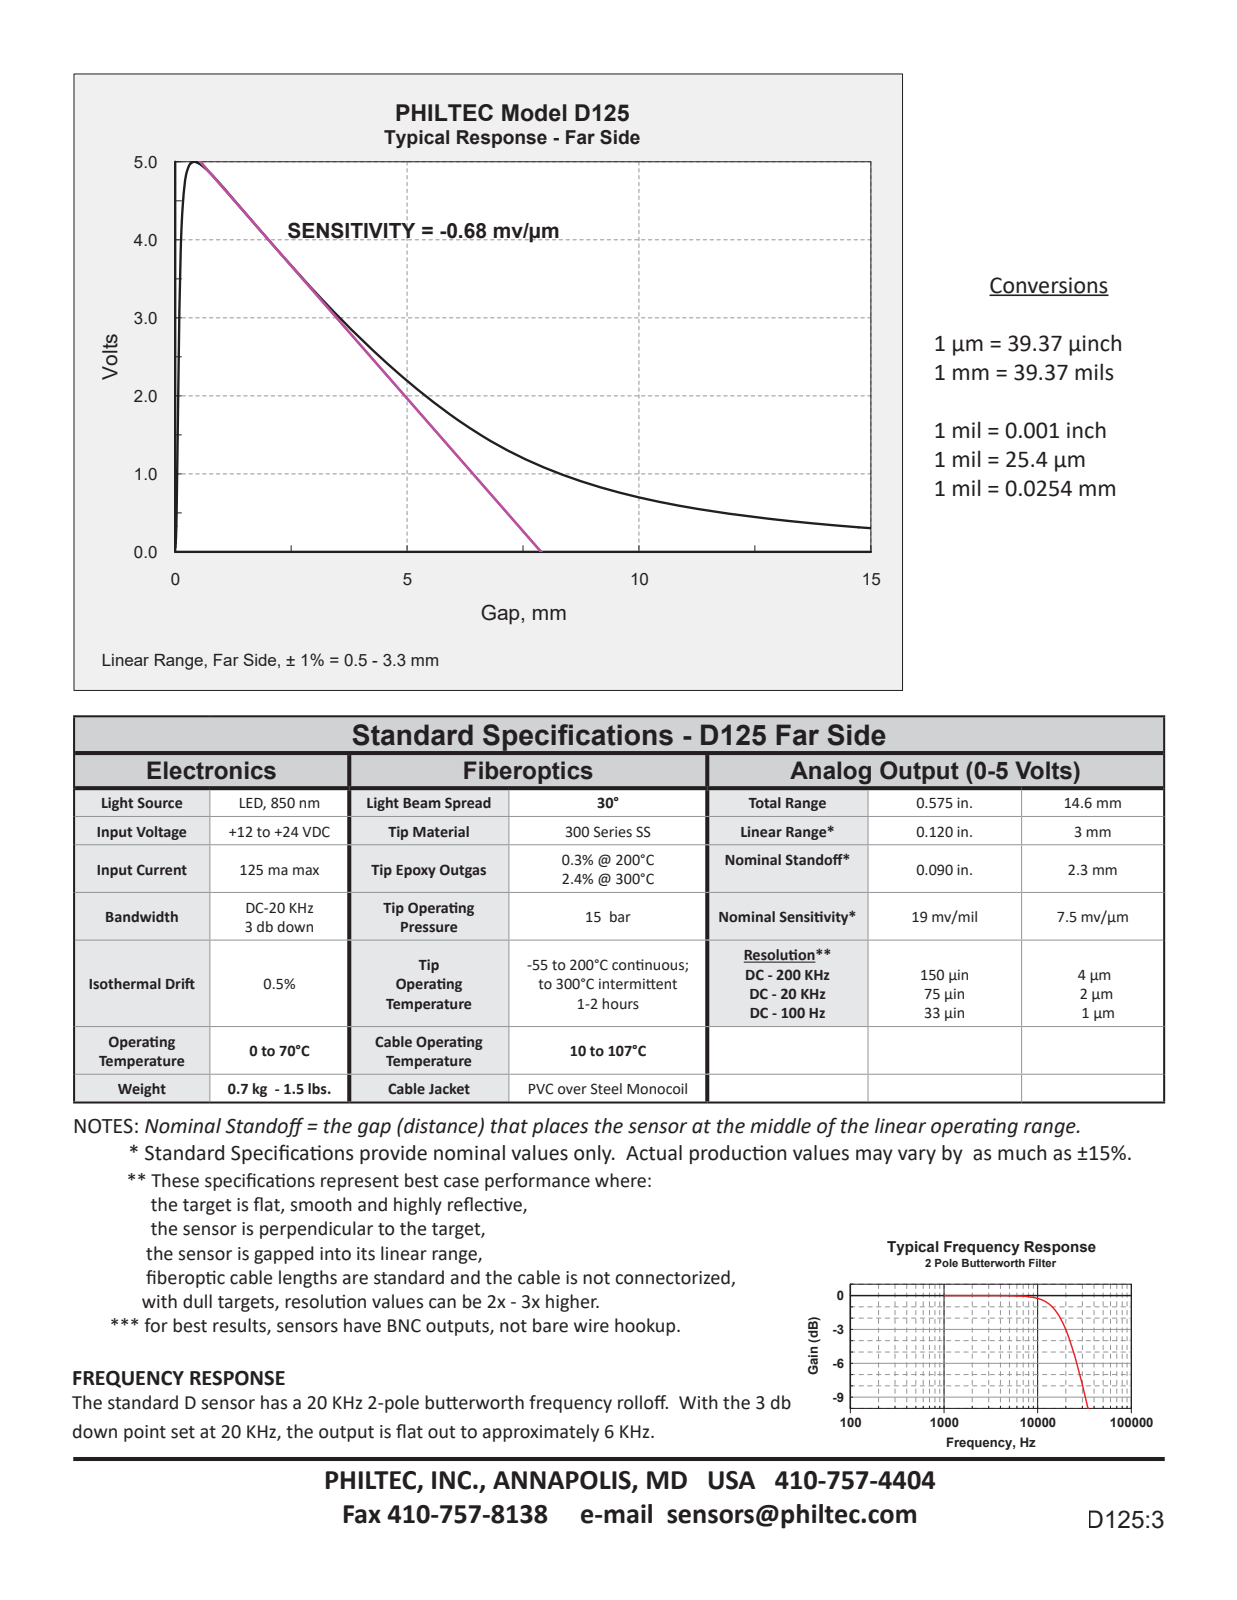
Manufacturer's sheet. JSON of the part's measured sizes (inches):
{"part_name": "D125", "step_written_by": "SolidWorks 2018 (CONFIG_CONTROL_DESIGN)", "units": "inches", "bodies": {"solids": 1, "faces": 21, "planar": 5, "cylindrical": 12, "other": 4}, "overall_size": [10.306, 2.506, 0.28], "volume_in3": 0.435, "surface_area_in2": 8.008, "round_bosses_or_shafts": [[0.232, 3], [0.28, 1], [0.156, 1], [0.125, 1]], "face_to_face_distances": [7.306, 6.806, 0.5, 10.306, 3.5, 3]}
